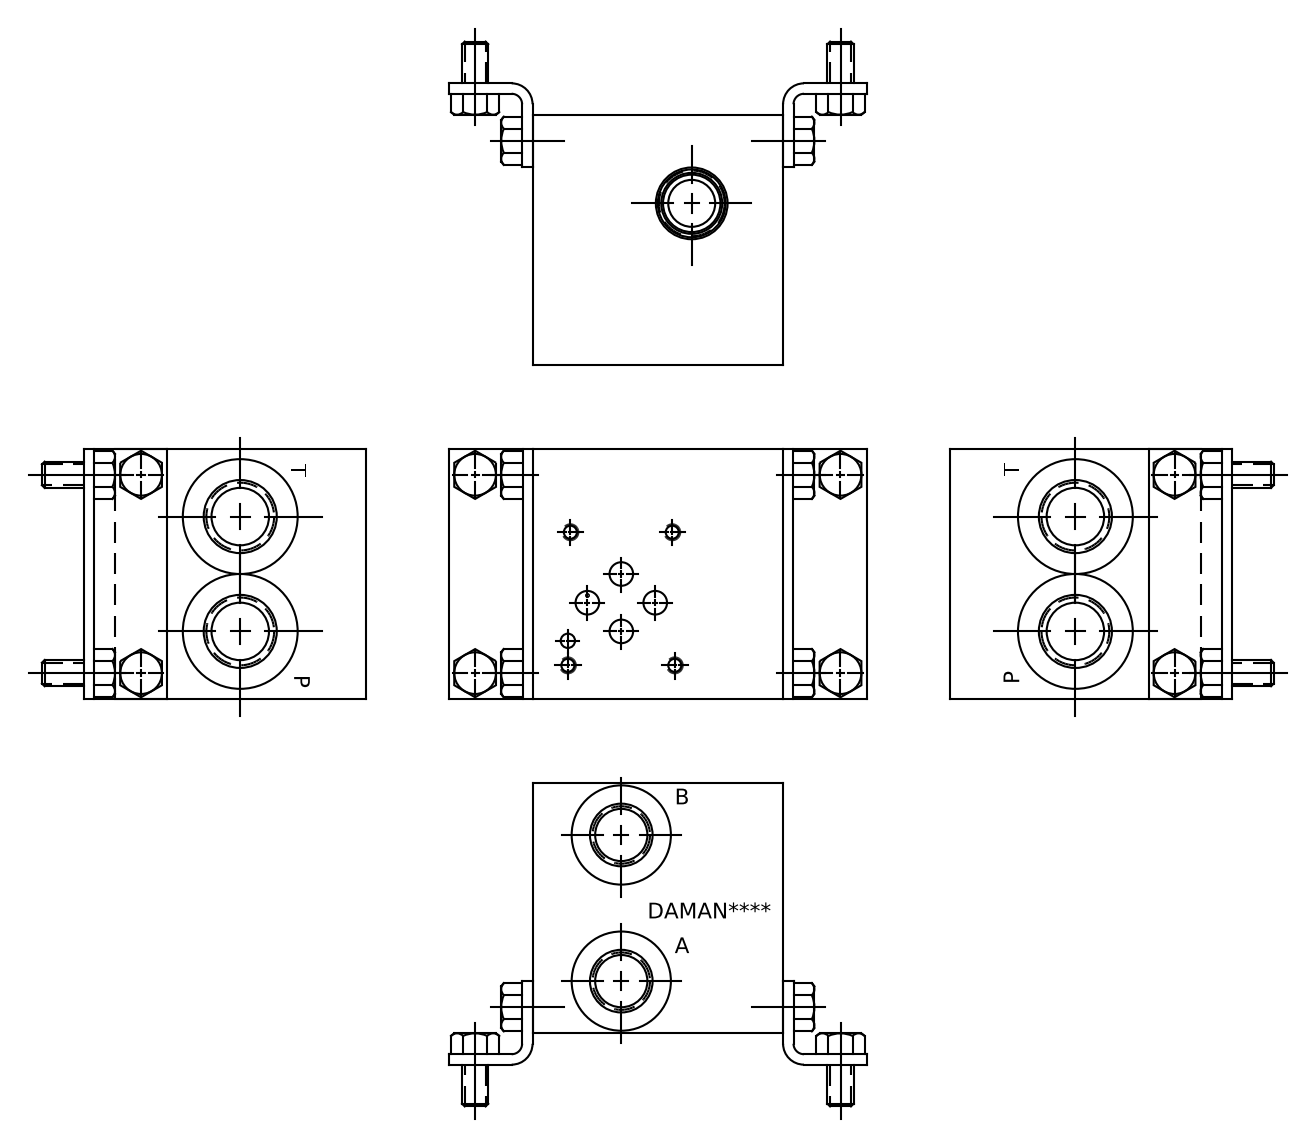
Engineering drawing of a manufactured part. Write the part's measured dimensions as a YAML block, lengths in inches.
part_name: "Part_AD03P012S~S_3D"
step_written_by: "Autodesk Inventor 2020 (CONFIG_CONTROL_DESIGN)"
units: inches
bodies: {solids: 1, faces: 549, planar: 311, cylindrical: 57, other: 181}
overall_size: [3, 3, 3]
volume: 22.69
surface_area: 76.67
round_holes:
  - {diameter: 0.149, count: 4}
  - {diameter: 0.19, count: 4}
  - {diameter: 0.281, count: 3}
  - {diameter: 0.257, count: 2}
  - {diameter: 0.312, count: 2}
  - {diameter: 0.625, count: 2}
  - {diameter: 0.688, count: 2}
  - {diameter: 0.689, count: 2}
  - {diameter: 0.75, count: 2}
  - {diameter: 0.758, count: 2}
  - {diameter: 0.805, count: 2}
  - {diameter: 0.875, count: 2}
face_to_face_distances: [3, 0.031, 2.969, 2.938, 0.687, 2.313, 0.656, 2.282, 0.03, 2.998]
hole_center_spacings: [0.785, 0.868, 1.283, 1.321, 1.594, 2.026, 2.233, 0.295]
